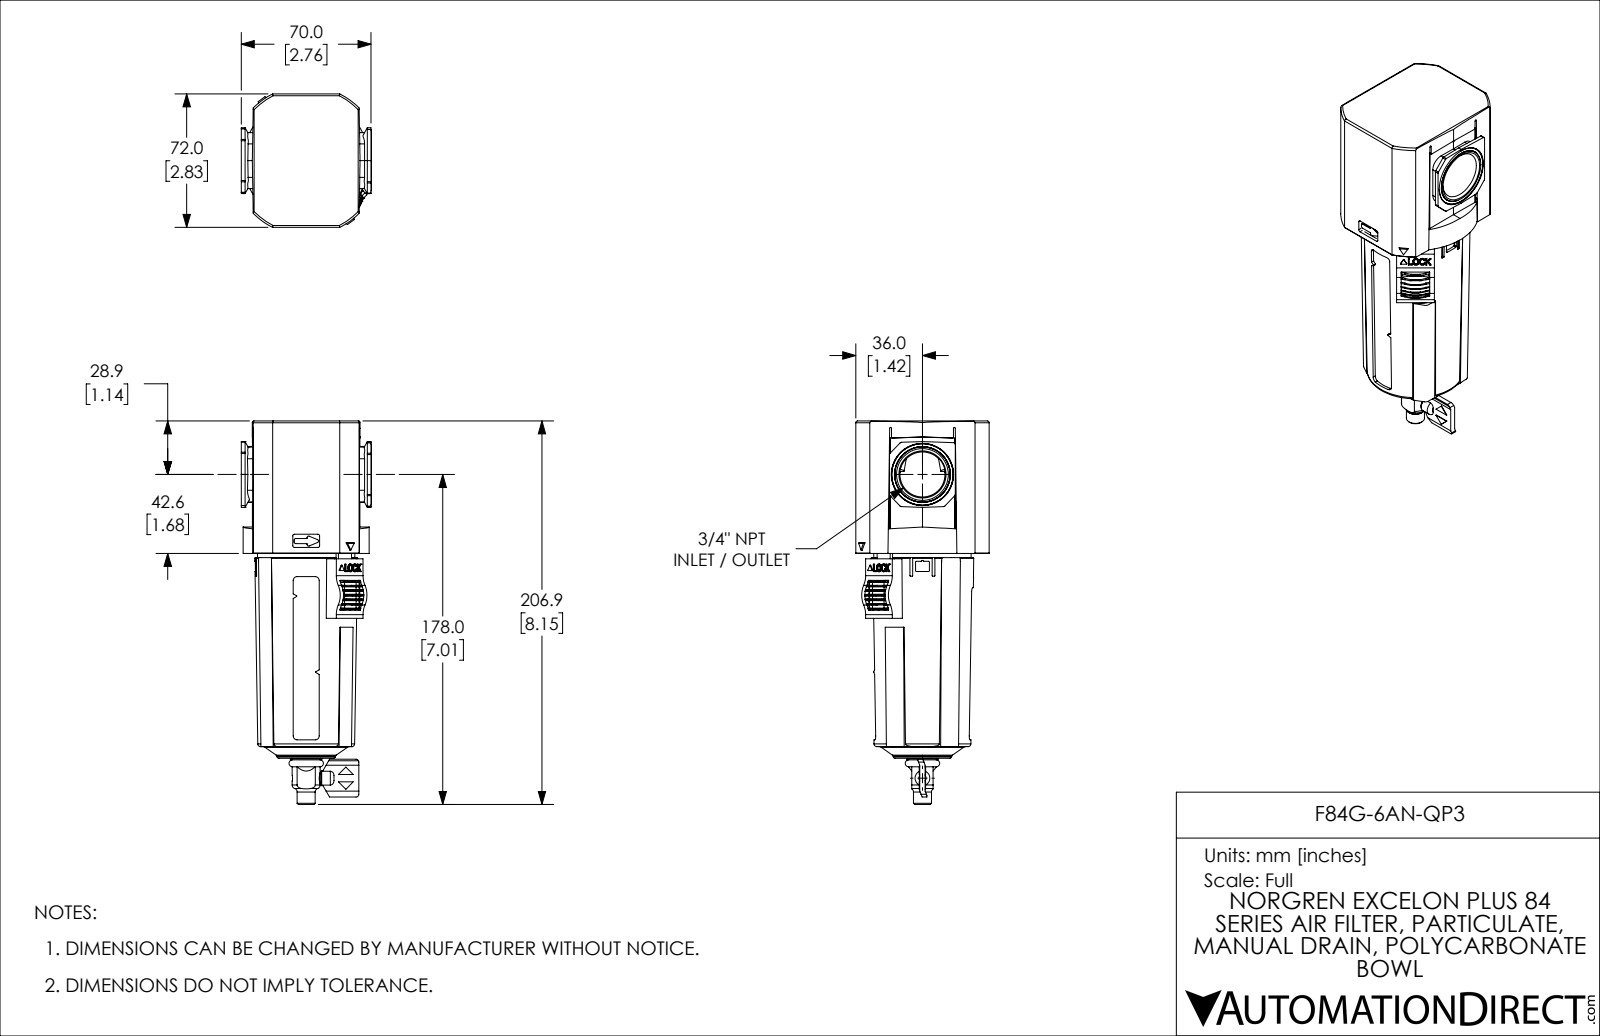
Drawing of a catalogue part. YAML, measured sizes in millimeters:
part_name: "F84G-6AN-QP3"
step_written_by: "SolidWorks 2021 (CONFIG_CONTROL_DESIGN)"
units: millimeters
bodies: {solids: 5, faces: 1065, planar: 481, cylindrical: 382, other: 202}
overall_size: [206.9, 72, 70.3]
volume: 449000
surface_area: 97100
round_holes:
  - {diameter: 4.1, count: 2}
  - {diameter: 3.1, count: 1}
  - {diameter: 3.2, count: 1}
  - {diameter: 6, count: 1}
  - {diameter: 6.4, count: 1}
  - {diameter: 9.5, count: 1}
  - {diameter: 24.6, count: 1}
  - {diameter: 62.5, count: 1}
round_bosses_or_shafts:
  - {diameter: 8, count: 3}
  - {diameter: 7, count: 2}
  - {diameter: 23, count: 1}
  - {diameter: 15.9, count: 1}
  - {diameter: 10.1, count: 1}
  - {diameter: 9.7, count: 1}
  - {diameter: 5.6, count: 1}
partial_cylinders:
  - {radius: 0.5, count: 40}
  - {radius: 1, count: 33}
  - {radius: 0.3, count: 24}
  - {radius: 0.7, count: 16}
  - {radius: 0.2, count: 10}
  - {radius: 1, count: 8}
  - {radius: 1.1, count: 8}
  - {radius: 1.5, count: 8}
face_to_face_distances: [1.5, 59.7, 61.2, 72, 0.9, 58.9, 60.4, 70, 10.3, 11.2]
hole_center_spacings: [15.1, 30.2]
